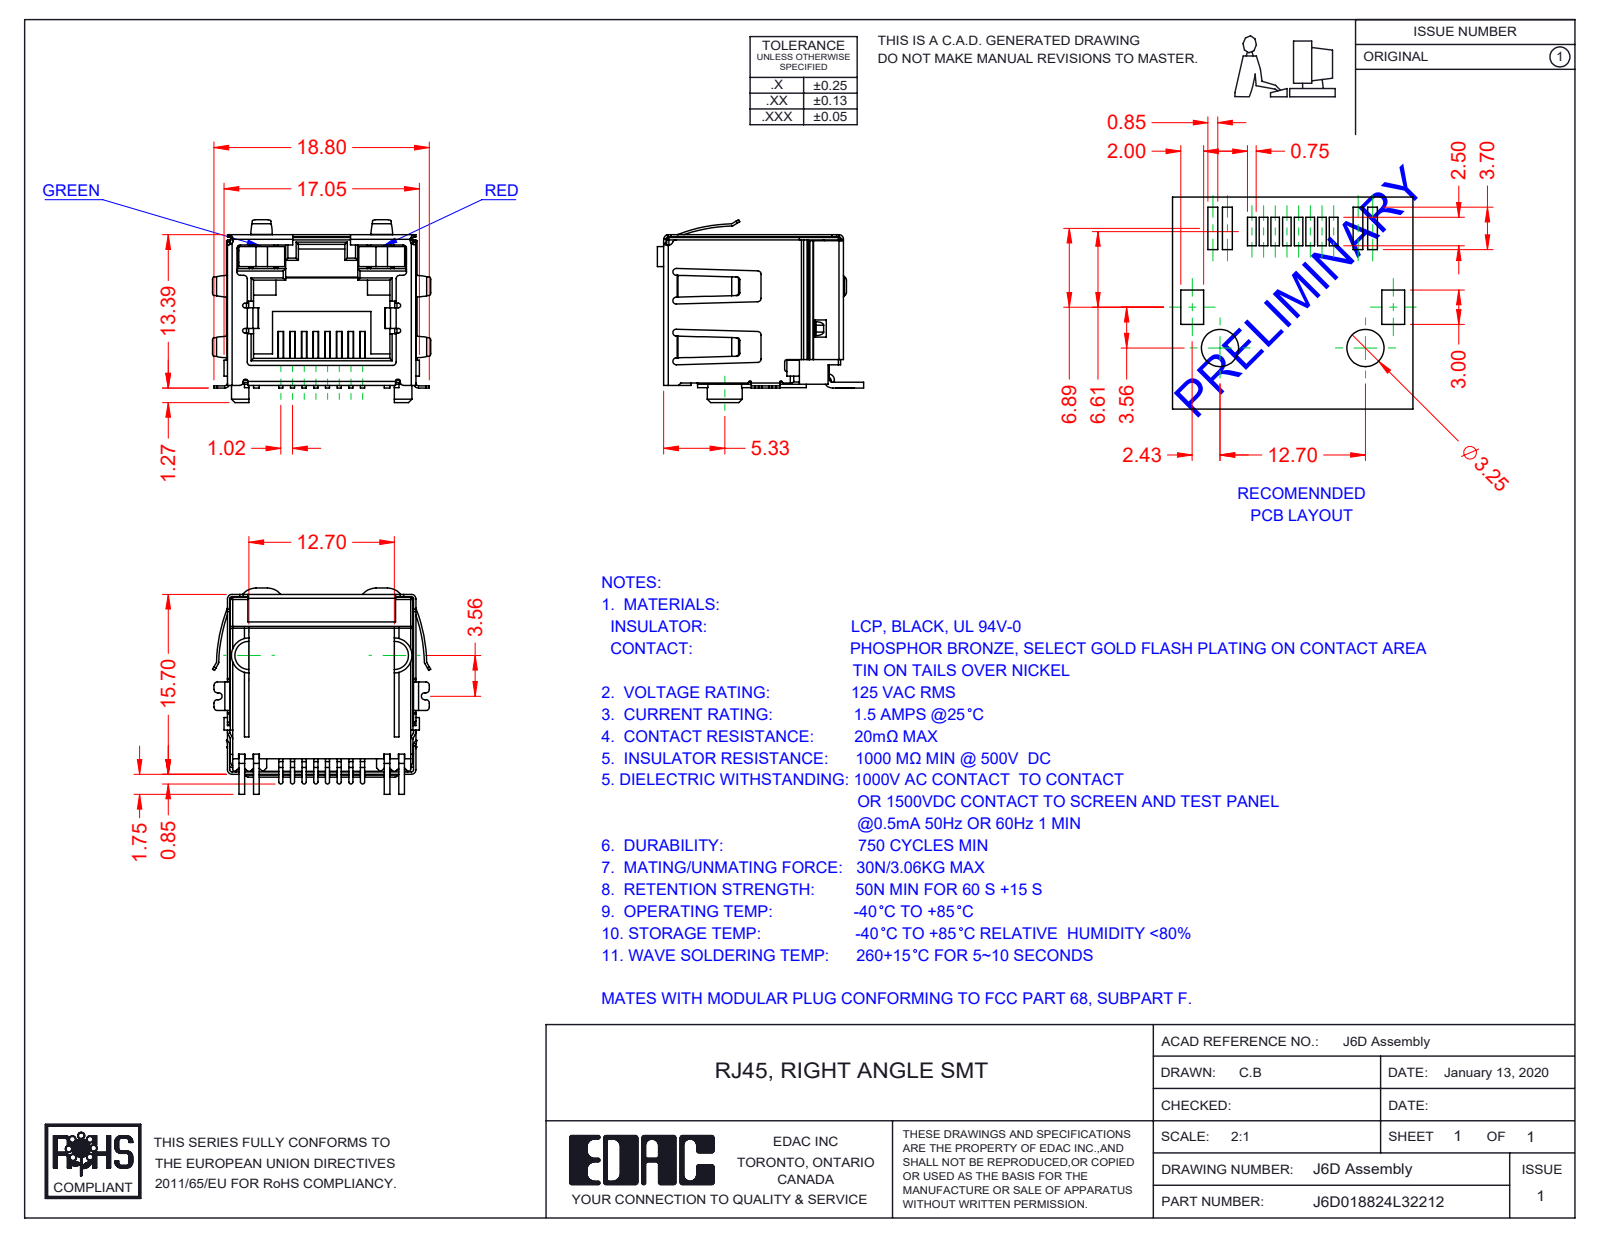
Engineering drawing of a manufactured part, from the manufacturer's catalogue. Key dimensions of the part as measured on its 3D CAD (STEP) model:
Part name (STEP PRODUCT): J6D018824L32212; 6D LED RH_2-Red; 6D Contacts; 6D LED LH_3-Green (+2 more)
STEP written by: SolidWorks 2016 (CONFIG_CONTROL_DESIGN)
Units: millimetres
Bodies: 12 solids, 1028 faces (701 planar, 282 cylindrical, 45 other)
Overall size (bounding box): 19.06 × 18 × 15.95
Volume: 1 790 mm³ · Surface area: 4 796 mm²
Partial cylindrical surfaces — rounded edges, fillets, slot ends (radius × count): R0.3 ×55, R0.2 ×40, R0.4 ×19, R0.25 ×16, R0.1 ×12, R0.15 ×8, R0.18 ×8, R0.5 ×6
Main face-to-face distances: 16, 16.2, 16.25, 2.25, 1, 15.95, 12.8, 0.45, 13.05, 10.6
